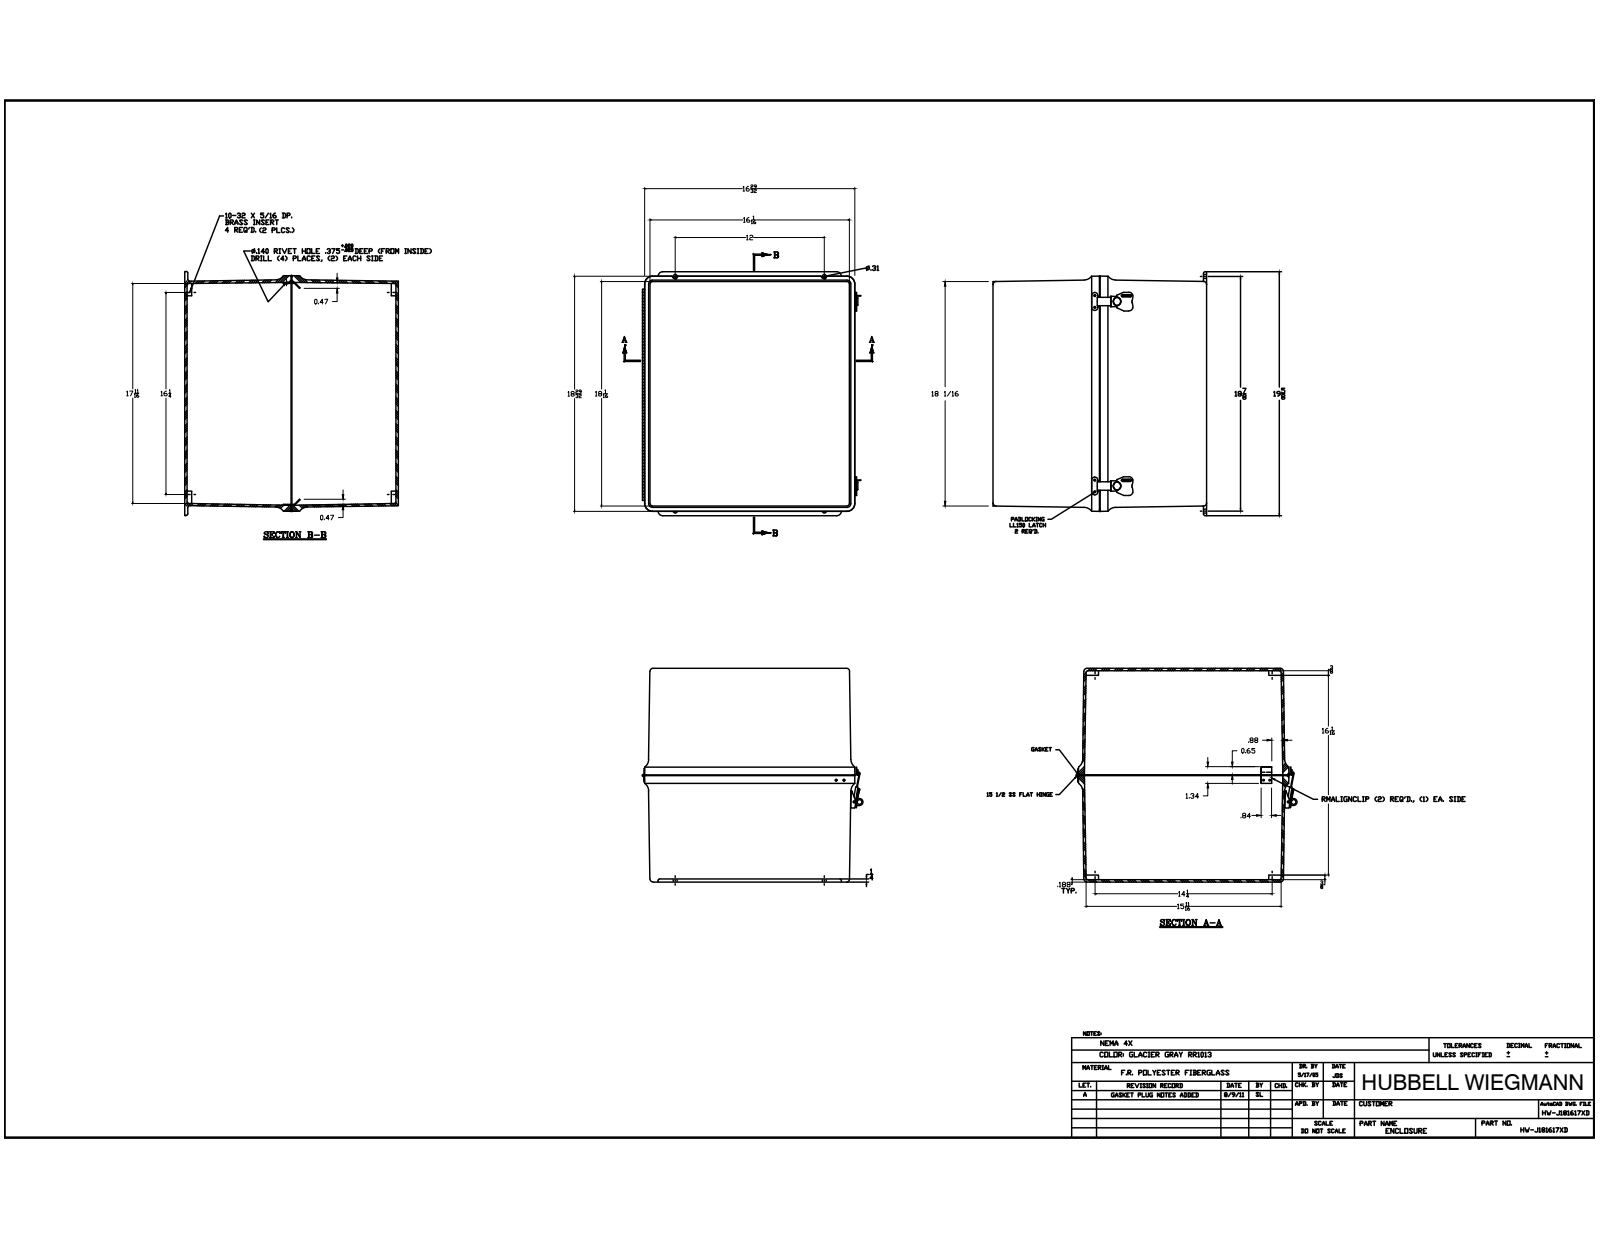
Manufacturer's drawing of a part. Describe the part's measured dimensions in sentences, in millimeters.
The part is named "J1816SSH; RMINS45821P_145; RMINS45821P_146; RMINS45821P_147 (+8 more)". Its 3-D file was written by "Autodesk Inventor 2014 (AUTOMOTIVE_DESIGN)". It is 62 solids with 1739 faces: 710 planar, 673 cylindrical and 356 other. Overall it measures 498.48 by 448.94 by 436.49 millimeters. Its volume is 5 947 000 cubic millimeters and its surface area 2 376 000 square millimeters. Round holes: 26 of diameter 3.56, 12 of diameter 3.45, 12 of diameter 3.86, 7 of diameter 3.96, 4 of diameter 3.3, 4 of diameter 4.2, 4 of diameter 5, 4 of diameter 5.54, 2 of diameter 3, 2 of diameter 3.5, 2 of diameter 4.9, 2 of diameter 13.5. Round bosses or shafts: 24 of diameter 6.35, 24 of diameter 3.17, 7 of diameter 6.86, 2 of diameter 14.8, 2 of diameter 13.3, 2 of diameter 5.3, 2 of diameter 4.7, 2 of diameter 3.25. Partial cylindrical surfaces (rounded edges, fillets, slot ends): 88 of radius 0.79, 19 of radius 2, 16 of radius 6.35, 14 of radius 19.05, 12 of radius 3.17, 8 of radius 0.95, 8 of radius 1, 8 of radius 1.15. The main face-to-face distances are 4.76, 409.6, 460.4, 404.84, 436.49, 4.77, 431.73, 426.96, 431.72, 455.64. The hole center spacings are 247.65, 380.59, 34.8, 85.72, 85.73, 171.45, 548.97, 387.33.
